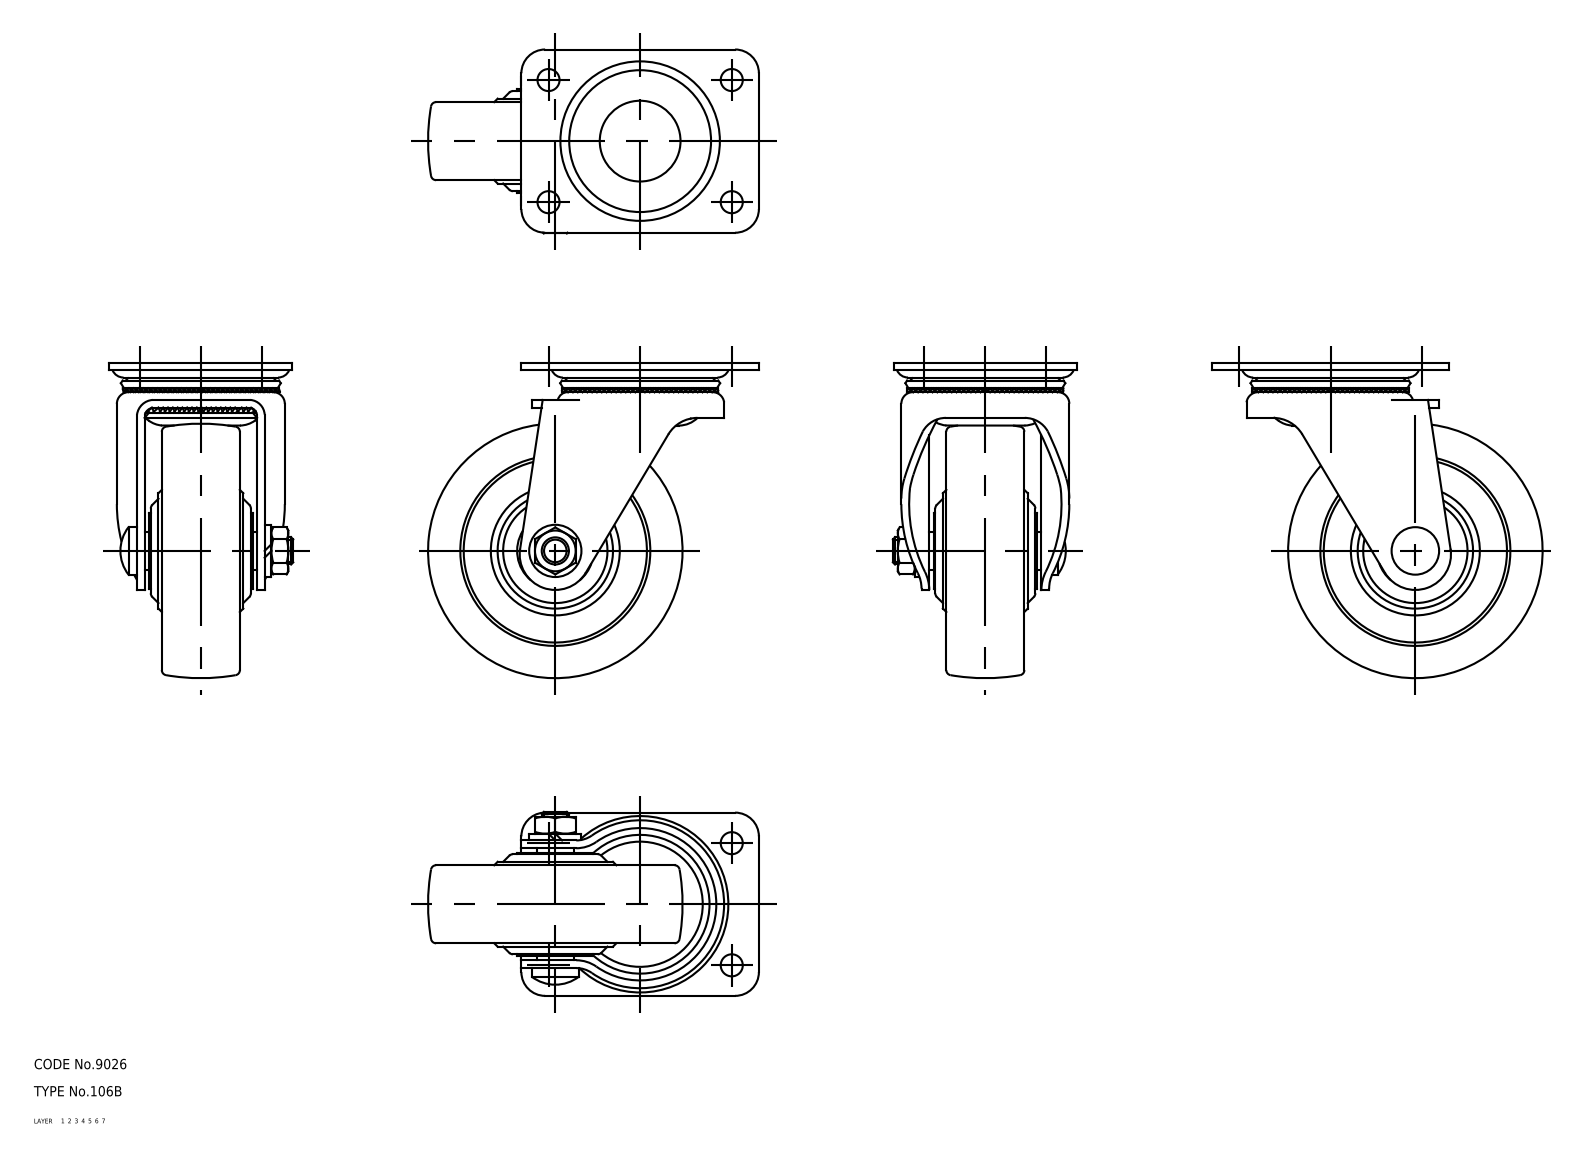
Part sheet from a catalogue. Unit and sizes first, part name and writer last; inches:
Units: inches
Overall size (bounding box): 3.839 × 3.661 × 2.135
Volume: 7.693 in³ · Surface area: 65.83 in²
Bodies: 4 solids, 222 faces (0 planar, 0 cylindrical, 222 other)
Part name (STEP PRODUCT): 67128725; 67128738; 67128751; 67128764 (+3 more)
STEP written by: CADfix (AUTOMOTIVE_DESIGN)
